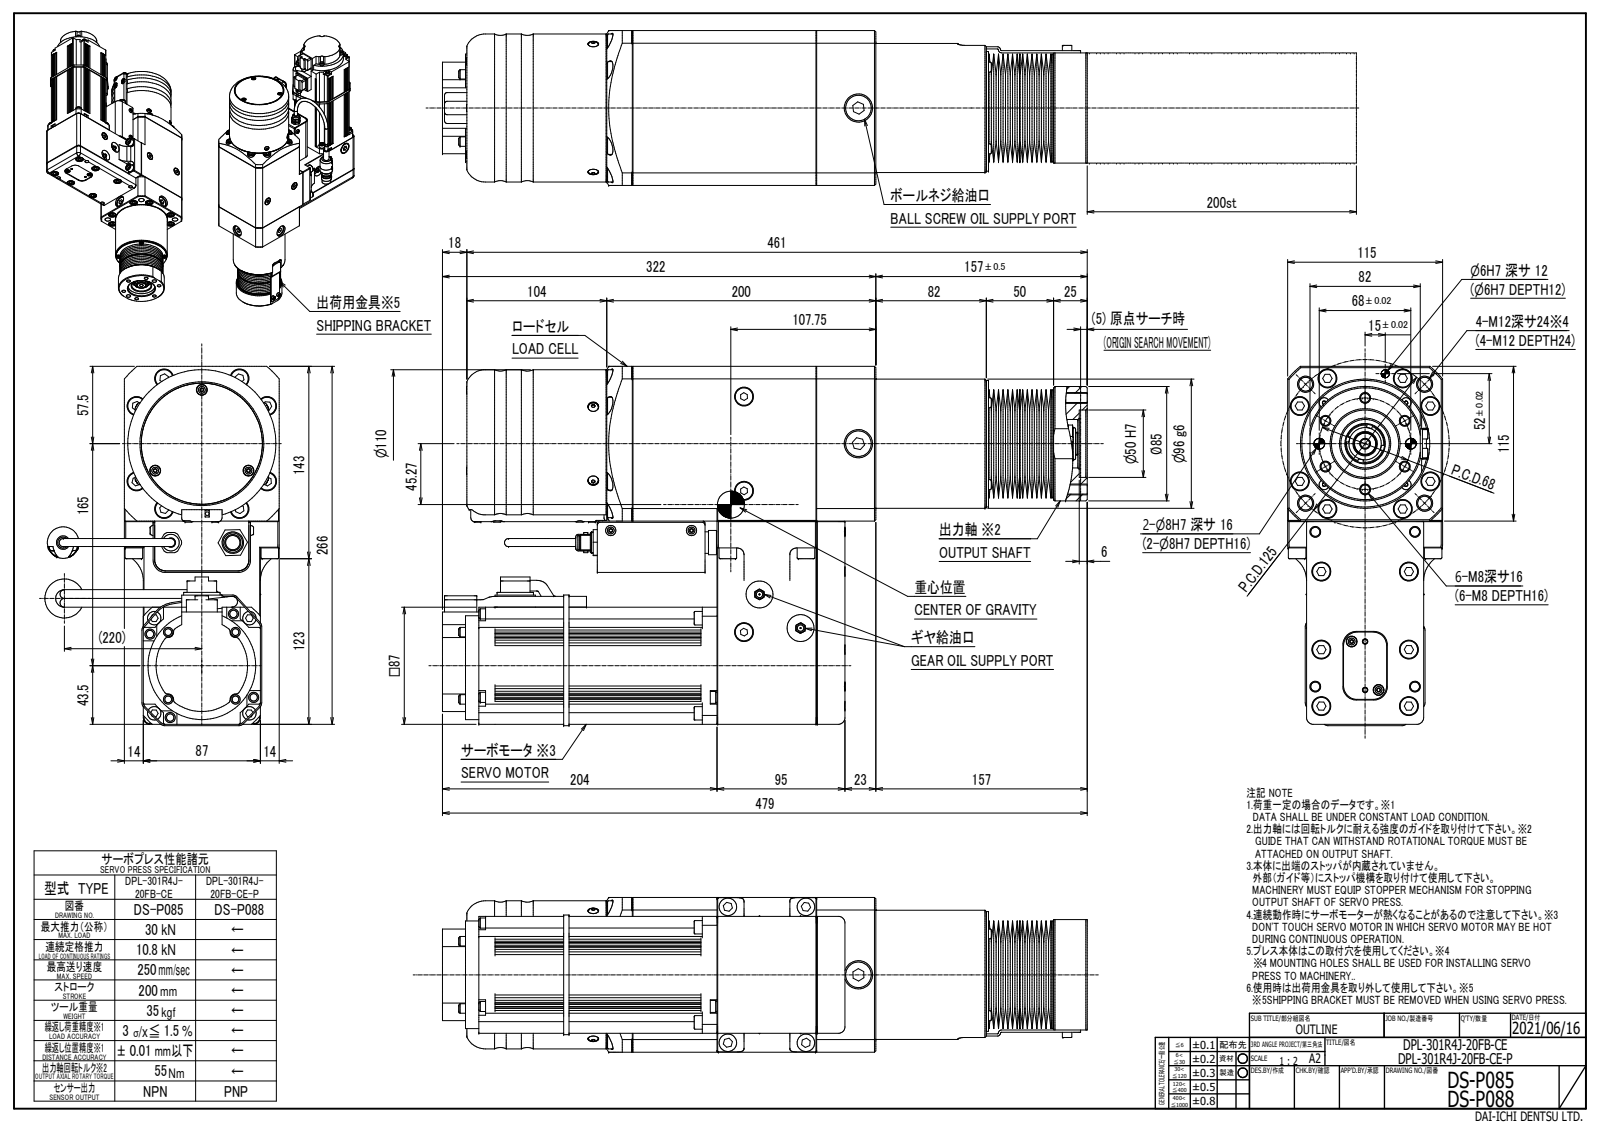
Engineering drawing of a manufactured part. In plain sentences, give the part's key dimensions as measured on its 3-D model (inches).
The part is named "DPL-301R4J-20FB-CE(DS-P085)". Its 3-D file was written by "Autodesk Inventor 2023 (CONFIG_CONTROL_DESIGN)". It is 16 solids with 2407 faces: 1493 planar, 557 cylindrical and 357 other. Overall it measures 18.858 by 10.512 by 6.781 inches. Its volume is 439.7 cubic inches and its surface area 964.1 square inches. Round holes: 14 of diameter 0.551, 13 of diameter 0.266, 12 of diameter 0.315, 8 of diameter 0.177, 6 of diameter 0.138, 4 of diameter 0.404, 3 of diameter 0.13, 2 of diameter 0.165, 2 of diameter 0.217, 2 of diameter 0.276, 2 of diameter 0.335, 2 of diameter 0.787. Round bosses or shafts: 21 of diameter 0.512, 8 of diameter 0.295, 6 of diameter 0.315, 6 of diameter 0.276, 6 of diameter 0.157, 5 of diameter 0.394, 5 of diameter 0.217, 4 of diameter 0.335. Partial cylindrical surfaces (rounded edges, fillets, slot ends): 48 of radius 0.024, 26 of radius 0.039, 21 of radius 0.197, 15 of radius 0.394, 13 of radius 0.118, 9 of radius 0.059, 9 of radius 0.079, 8 of radius 0.016. The main face-to-face distances are 0.551, 3.976, 4.528, 0.118, 3.425, 0.059, 0.177, 0.354, 0.236, 1.772. The hole center spacings are 1.339, 1.785, 3.536, 0.693, 1.218, 1.893, 2.319, 2.46.
